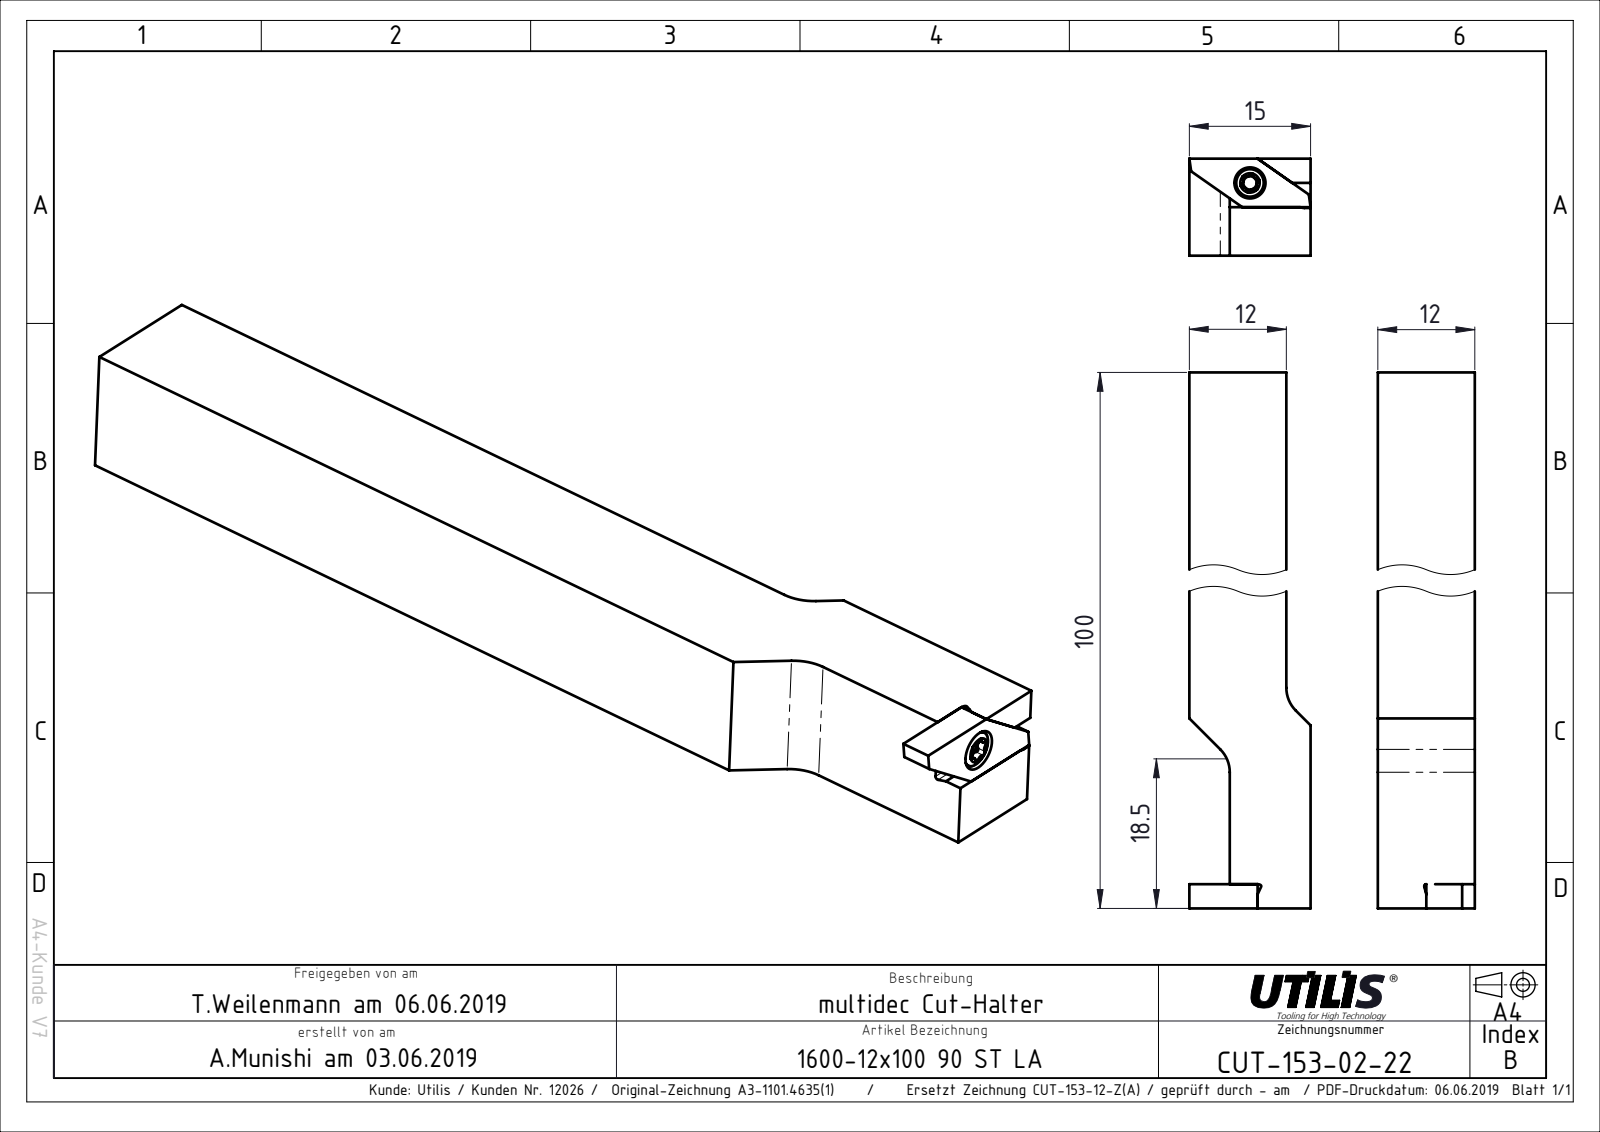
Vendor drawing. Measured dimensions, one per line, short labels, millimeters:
name: CUT-153-02-22
written by: SolidWorks 2018 (AUTOMOTIVE_DESIGN)
unit: mm
bodies: 1 solid, 15 faces (13 planar, 2 cylindrical, 0 other)
size: 100 × 15 × 12
volume: 14 064 mm³; area: 5 090 mm²
rounds: 2× R4
face distances: 12, 3, 15, 10, 7, 5, 100, 97
